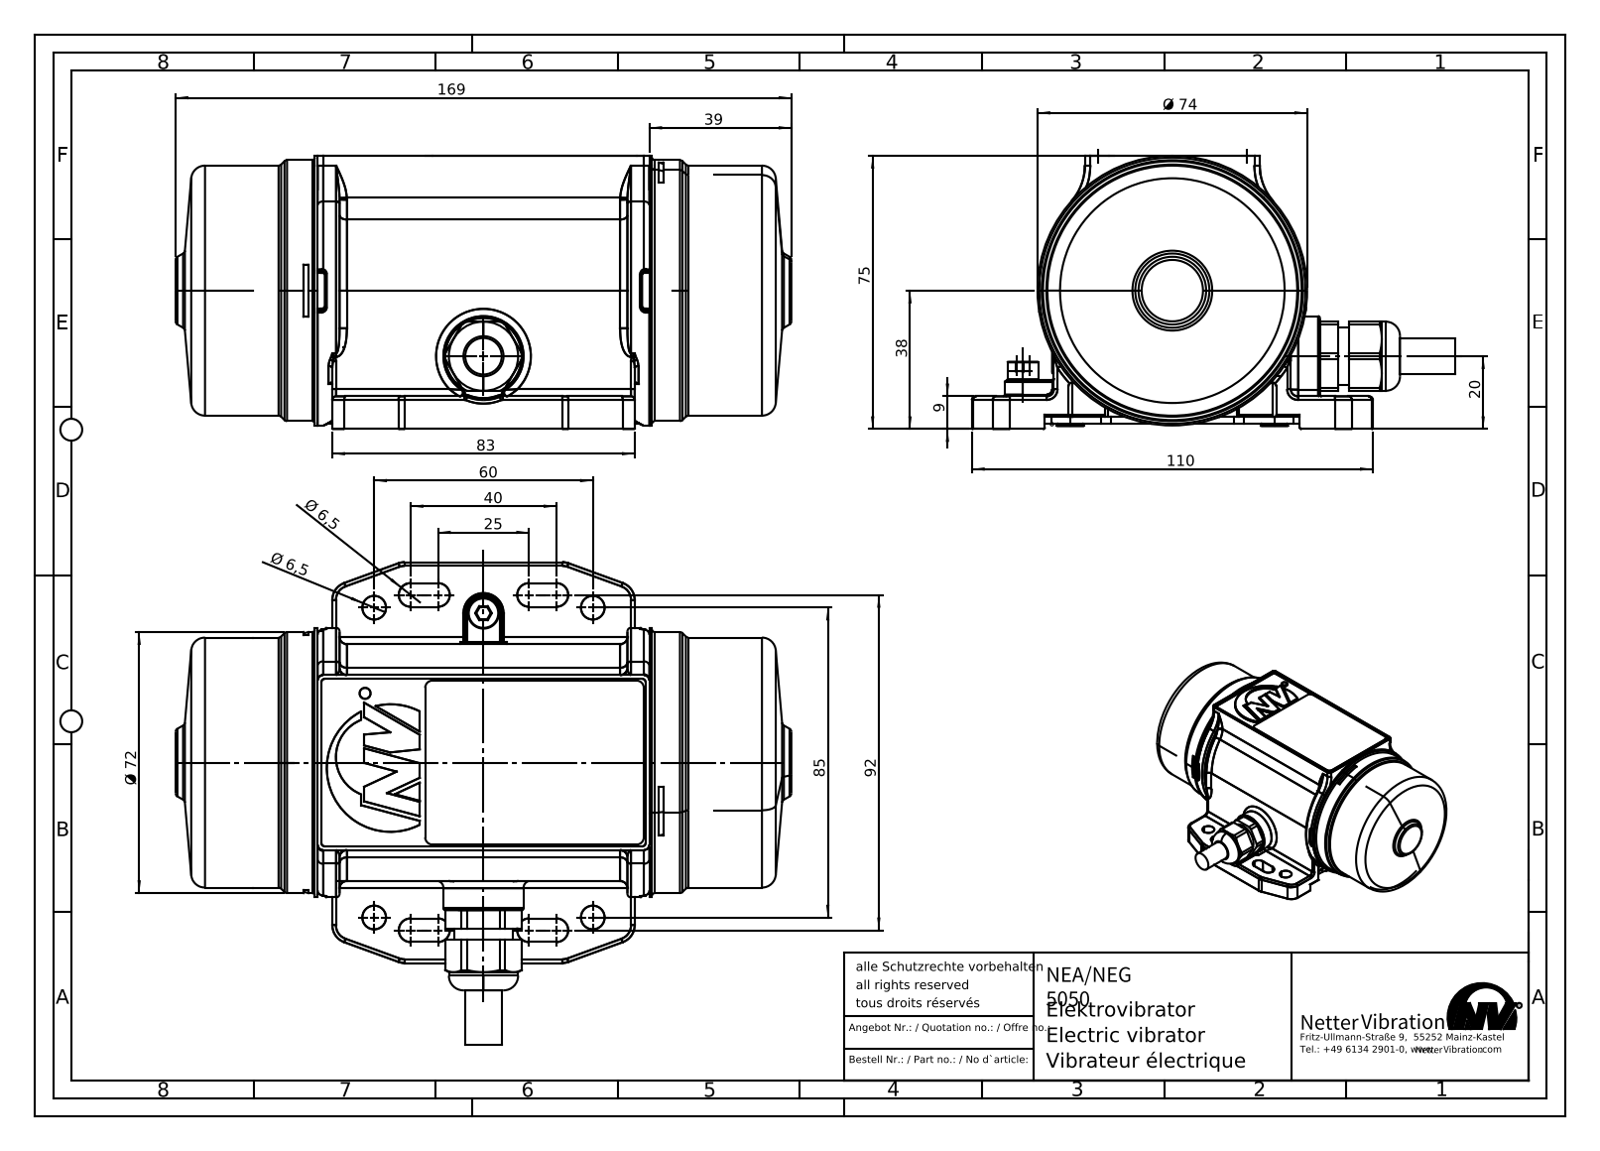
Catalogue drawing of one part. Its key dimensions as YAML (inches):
part_name: "NEA-NEG 5050"
step_written_by: "SolidWorks 2010 (AUTOMOTIVE_DESIGN)"
units: inches
bodies: {solids: 1, faces: 627, planar: 255, cylindrical: 207, other: 165}
overall_size: [6.654, 4.626, 2.953]
volume: 42.66
surface_area: 98.21
round_holes:
  - {diameter: 0.256, count: 4}
  - {diameter: 0.165, count: 1}
  - {diameter: 0.394, count: 1}
  - {diameter: 0.472, count: 1}
  - {diameter: 0.571, count: 1}
round_bosses_or_shafts:
  - {diameter: 0.295, count: 4}
  - {diameter: 2.913, count: 1}
  - {diameter: 2.819, count: 1}
  - {diameter: 2.701, count: 1}
  - {diameter: 0.866, count: 1}
  - {diameter: 0.748, count: 1}
  - {diameter: 0.63, count: 1}
  - {diameter: 0.512, count: 1}
partial_cylinders:
  - {radius: 0.039, count: 32}
  - {radius: 0.197, count: 29}
  - {radius: 0.079, count: 10}
  - {radius: 0.128, count: 8}
  - {radius: 0.02, count: 7}
  - {radius: 0.059, count: 4}
  - {radius: 0.394, count: 2}
  - {radius: 0.591, count: 2}
face_to_face_distances: [2.894, 0.059, 2.953, 0.354, 0.295, 2.598, 2.224, 0.335, 2.559, 0.079]
hole_center_spacings: [1.183, 2.362, 3.346, 3.493, 4.096, 0.079]
